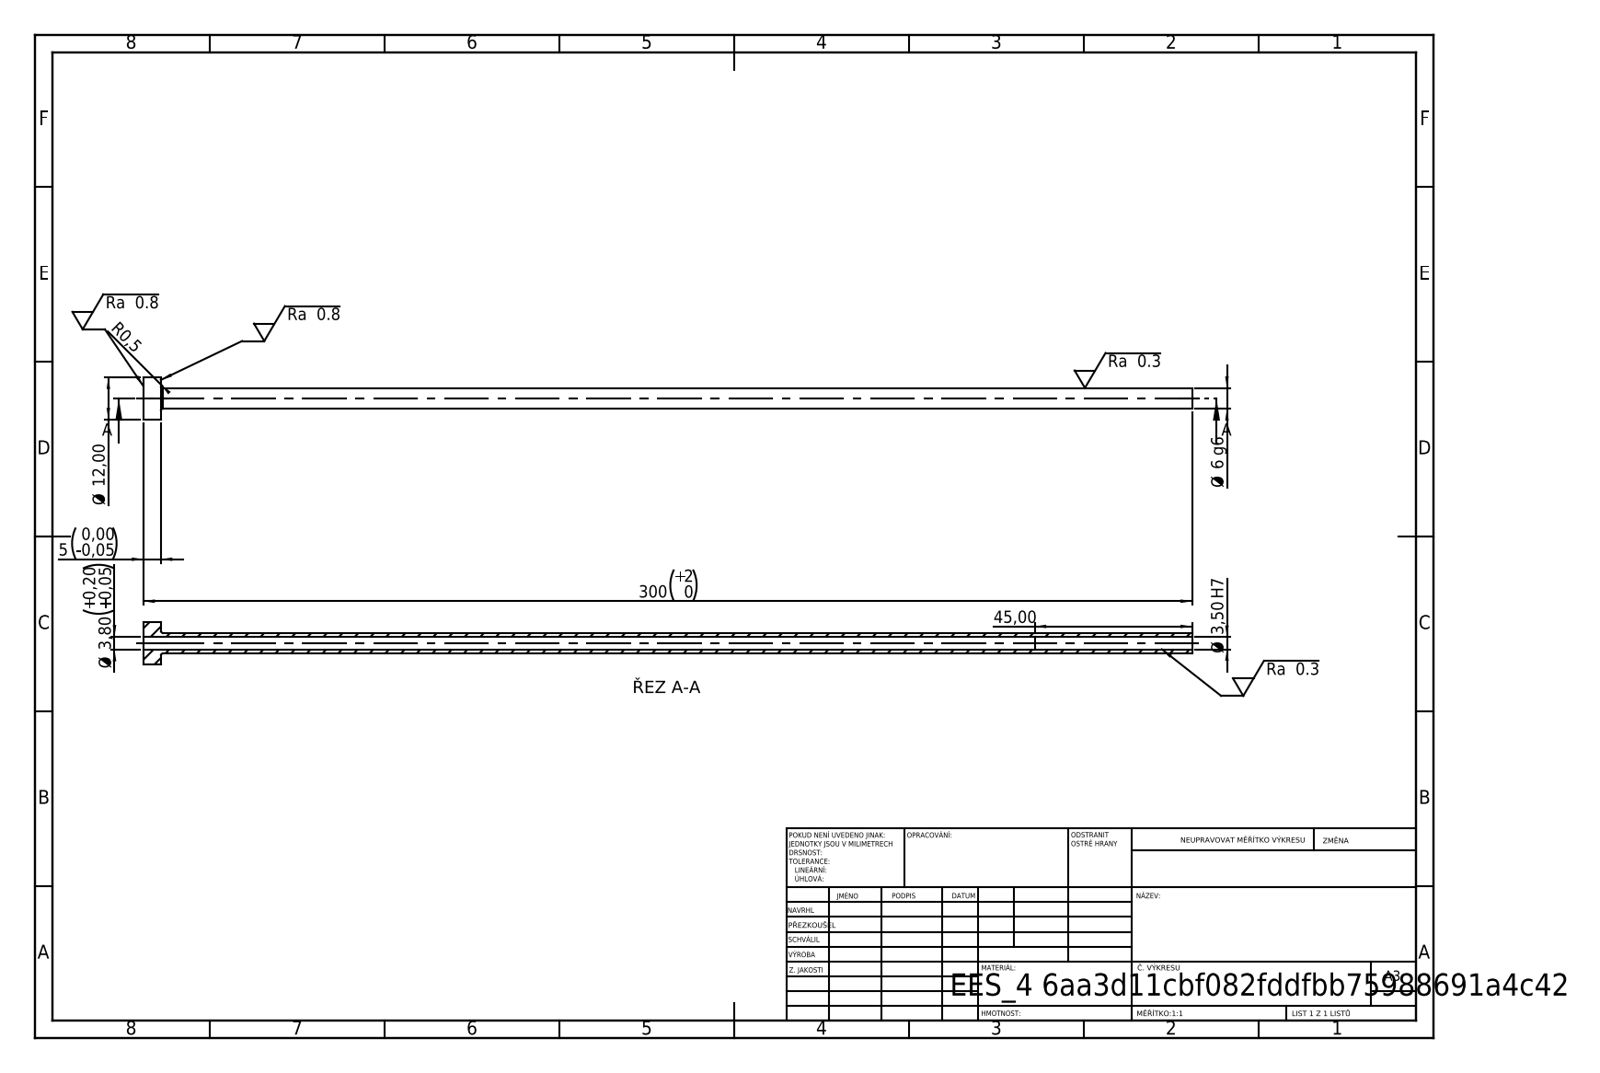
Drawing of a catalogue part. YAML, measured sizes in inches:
step_written_by: "SolidWorks 2019 (CONFIG_CONTROL_DESIGN)"
units: inches
bodies: {solids: 1, faces: 14, planar: 4, cylindrical: 8, other: 2}
overall_size: [11.811, 0.472, 0.472]
volume: 0.341
surface_area: 14.71
round_holes:
  - {diameter: 0.138, count: 1}
  - {diameter: 0.15, count: 1}
round_bosses_or_shafts:
  - {diameter: 0.472, count: 1}
  - {diameter: 0.236, count: 1}
face_to_face_distances: [0.197, 11.811, 11.614, 10.039, 9.843, 1.772]
